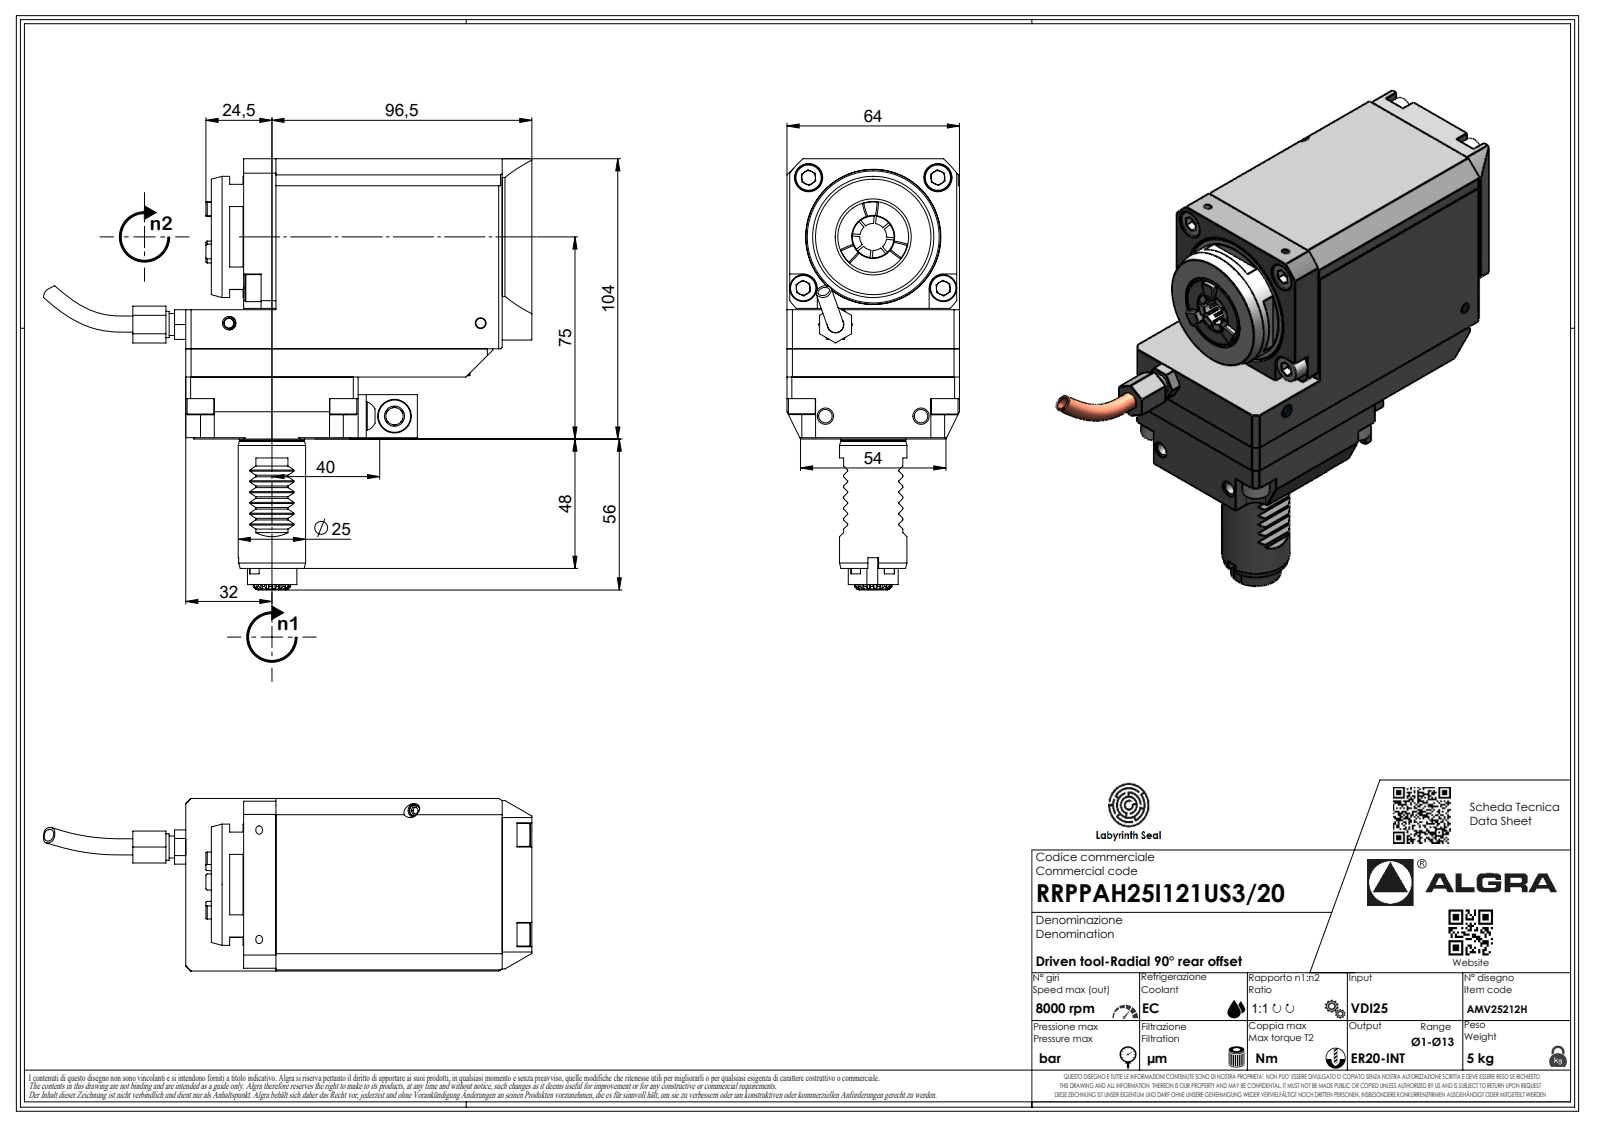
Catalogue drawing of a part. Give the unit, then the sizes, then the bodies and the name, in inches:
Units: inches
Overall size (bounding box): 7.138 × 6.299 × 2.52
Round holes (diameter × count): ⌀0.083 ×1, ⌀0.354 ×1
Round bosses / shafts (diameter × count): ⌀1.772 ×1, ⌀0.984 ×1, ⌀0.949 ×1, ⌀0.728 ×1, ⌀0.386 ×1, ⌀0.321 ×1, ⌀0.251 ×1, ⌀0.067 ×1
Partial cylindrical surfaces — rounded edges, fillets, slot ends (radius × count): R0.012 ×12, R0.013 ×7, R0.02 ×7, R0.146 ×7, R1.281 ×5, R0.207 ×2, R0.008 ×1, R0.242 ×1
Main face-to-face distances: 2.52, 4.094, 1.89, 5.059, 0.984, 3.189, 0.906, 2.205, 4.213, 0.846
Volume: 43.08 in³ · Surface area: 93.5 in²
Bodies: 1 solid, 733 faces (482 planar, 122 cylindrical, 129 other)
Part name (STEP PRODUCT): RRPPAH25I121US320
STEP written by: SolidWorks 2023 (AUTOMOTIVE_DESIGN)
